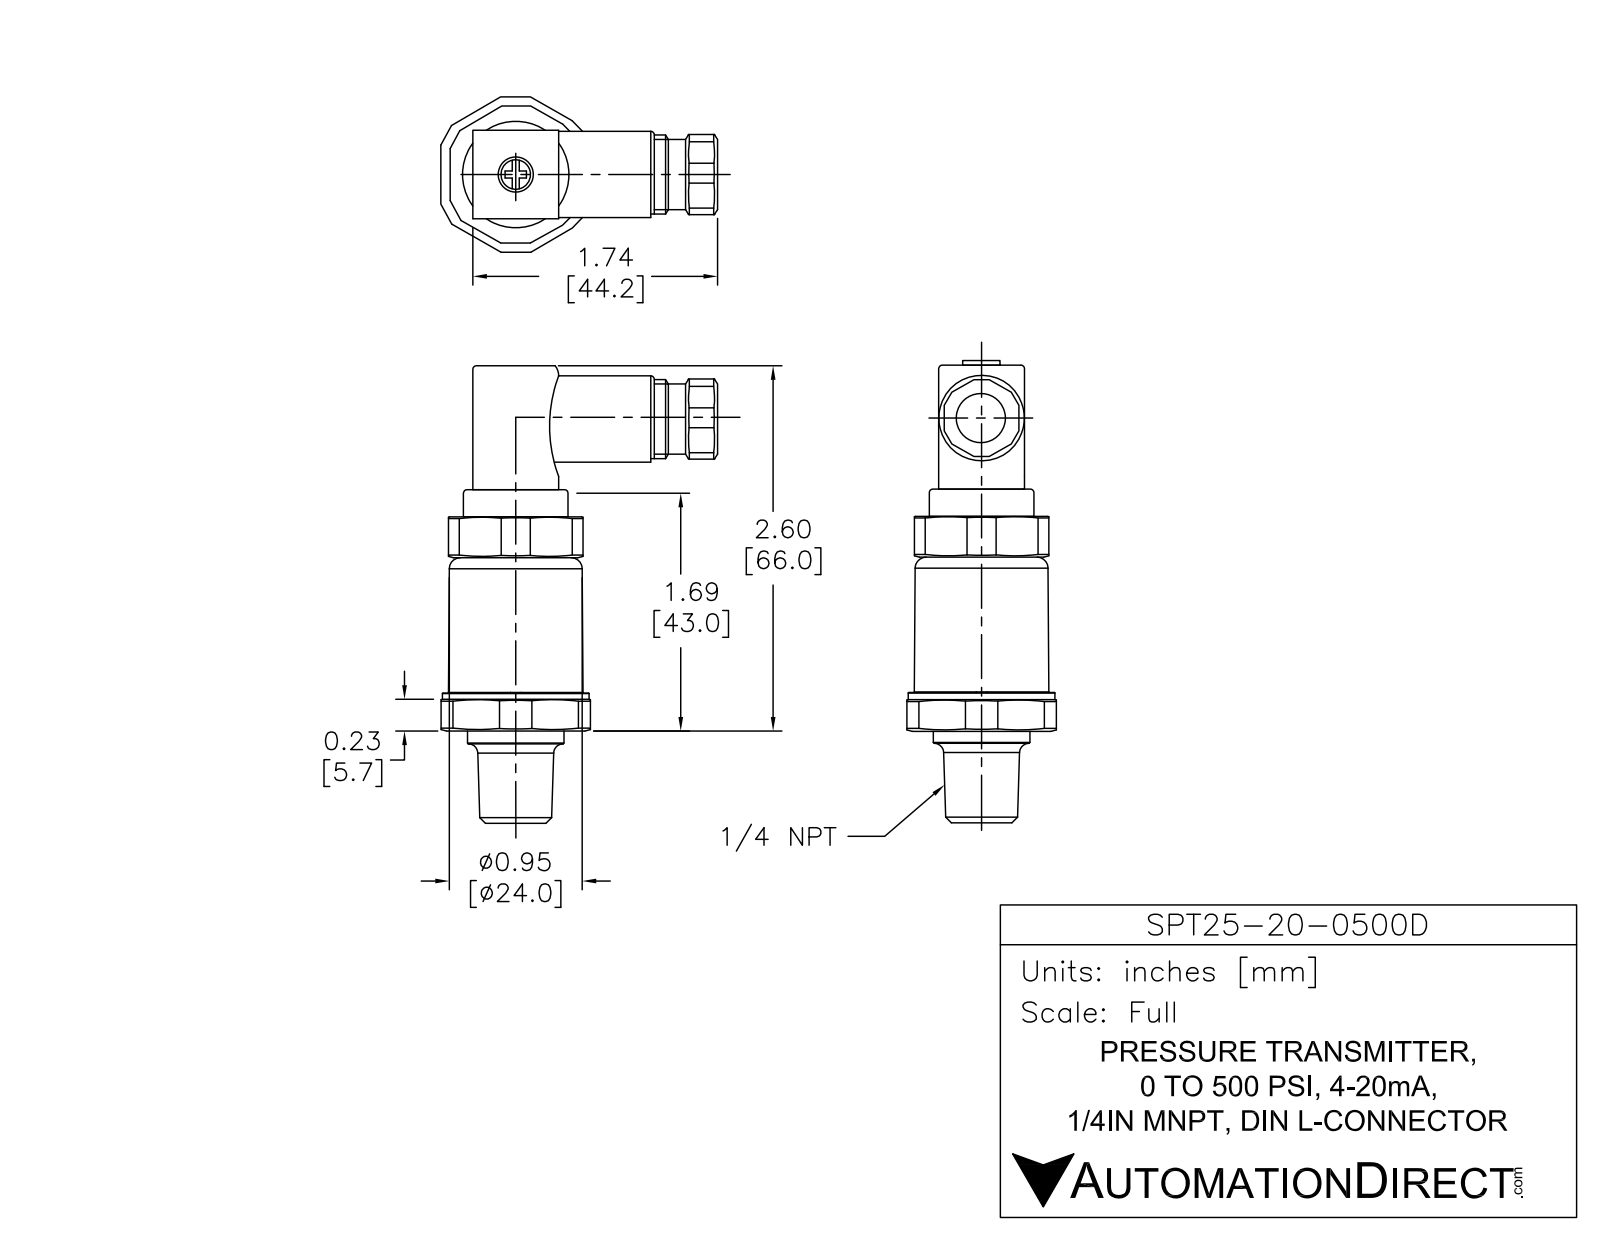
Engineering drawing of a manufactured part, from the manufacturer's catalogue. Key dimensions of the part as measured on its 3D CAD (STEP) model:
Part name (STEP PRODUCT): SPT25-20-0500D
STEP written by: SolidWorks 2013 (AUTOMOTIVE_DESIGN)
Units: millimetres
Bodies: 5 solids, 200 faces (96 planar, 87 cylindrical, 17 other)
Overall size (bounding box): 81.25 × 38.01 × 35.71
Volume: 27 893 mm³ · Surface area: 10 133 mm²
Round holes (diameter × count): ⌀1 ×1, ⌀3.3 ×1, ⌀7 ×1, ⌀8 ×1
Round bosses / shafts (diameter × count): ⌀26.75 ×1, ⌀24 ×1, ⌀17.5 ×1, ⌀15 ×1, ⌀14 ×1, ⌀11 ×1
Partial cylindrical surfaces — rounded edges, fillets, slot ends (radius × count): R1.5 ×8, R1.15 ×4, R2.25 ×4, R2 ×3, R1.15 ×1, R1.17 ×1, R14.5 ×1
Main face-to-face distances: 1.5, 29.5, 31, 15.75, 0.35, 15.4, 6.75, 37.75, 36.25, 5
Hole centre spacings: 1.33
